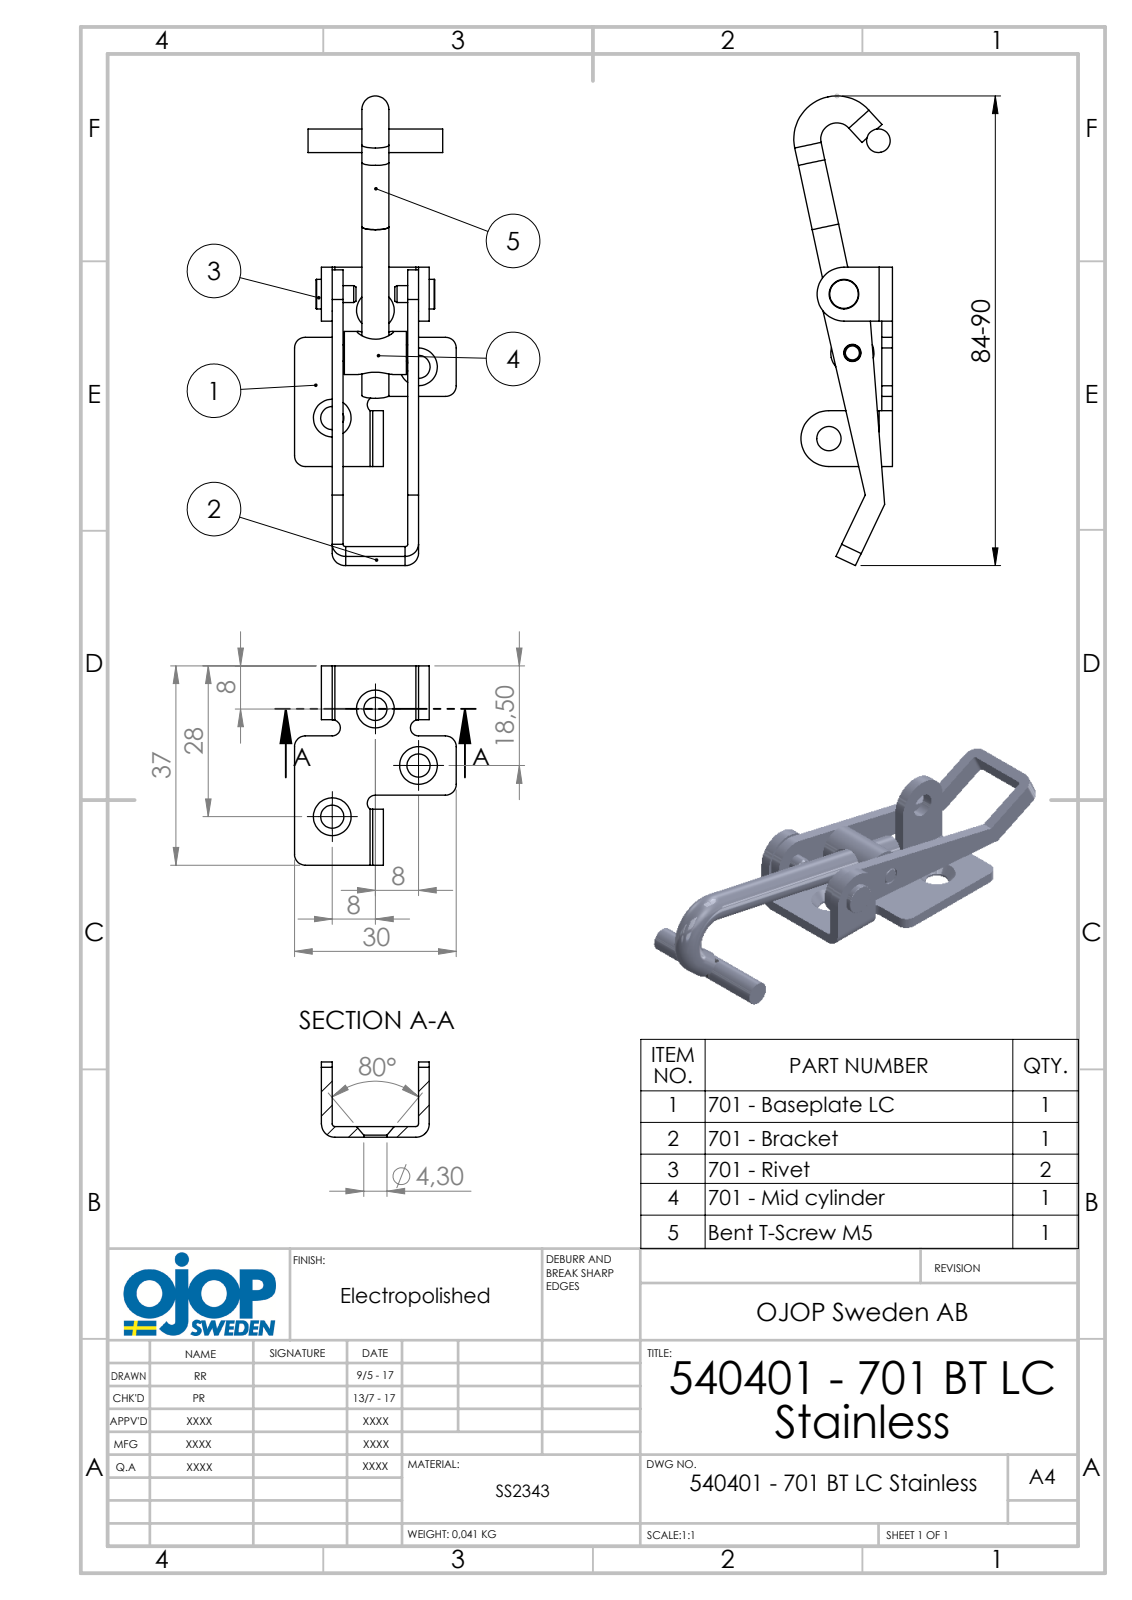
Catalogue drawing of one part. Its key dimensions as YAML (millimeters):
part_name: "701 - LC; 701 - Mid Cylinder; Böjd T-skruv M5_Default<As Machined>; 540401 - 701 TLC RF (+2 more)"
step_written_by: "SolidWorks 2015 (AUTOMOTIVE_DESIGN)"
units: millimeters
bodies: {solids: 6, faces: 164, planar: 65, cylindrical: 75, other: 24}
overall_size: [91.6, 30, 19.26]
volume: 5614
surface_area: 6683
round_holes:
  - {diameter: 4.3, count: 3}
  - {diameter: 3.2, count: 2}
  - {diameter: 4.5, count: 2}
  - {diameter: 4.8, count: 1}
round_bosses_or_shafts:
  - {diameter: 5, count: 2}
  - {diameter: 8, count: 1}
  - {diameter: 5.5, count: 1}
  - {diameter: 5.01, count: 1}
  - {diameter: 4.38, count: 1}
  - {diameter: 3.15, count: 1}
  - {diameter: 3, count: 1}
partial_cylinders:
  - {radius: 0.5, count: 5}
  - {radius: 2.5, count: 5}
  - {radius: 2, count: 4}
  - {radius: 1.5, count: 3}
  - {radius: 4.5, count: 1}
  - {radius: 5, count: 1}
  - {radius: 5.19, count: 1}
face_to_face_distances: [2, 14, 16, 12, 4, 6.5, 7.5, 9.5, 8.5, 18]
hole_center_spacings: [11.02, 13.2, 16.49, 18.61, 21.54, 26.96]
